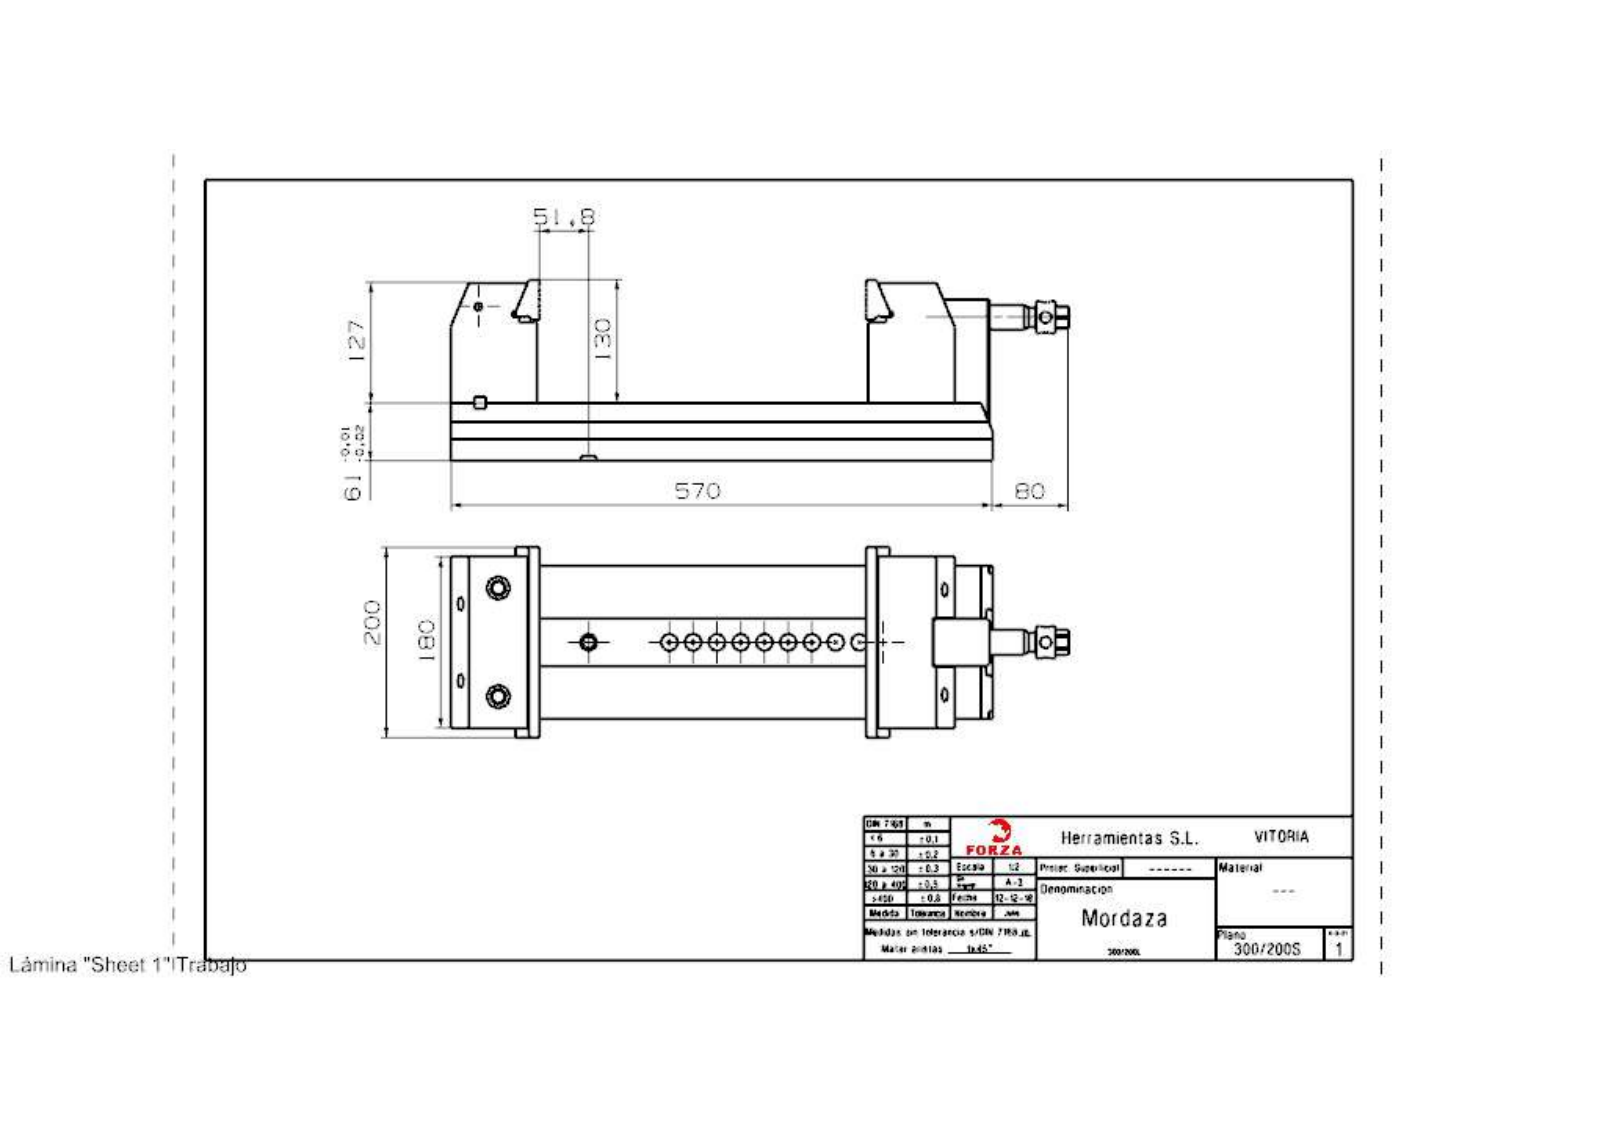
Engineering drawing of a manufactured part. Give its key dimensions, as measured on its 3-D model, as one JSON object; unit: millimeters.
{"part_name": "300_200S_Mordaza", "step_written_by": "SIEMENS PLM Software NX 11.0 (AUTOMOTIVE_DESIGN)", "units": "millimeters", "bodies": {"solids": 10, "faces": 481, "planar": 268, "cylindrical": 138, "other": 75}, "overall_size": [650, 200, 191], "volume_mm3": 8427000, "surface_area_mm2": 743184, "round_holes": [[15, 6], [5.19, 5], [13, 5], [6.99, 4], [8.5, 4], [10, 4], [8.78, 3], [10.58, 3], [19, 3], [12, 2], [12.38, 2], [14.38, 2]], "round_bosses_or_shafts": [[34, 1], [33.8, 1], [26, 1], [20, 1], [16.5, 1]], "partial_cylinders_radius": [[0.4, 24], [1.5, 4], [8, 4], [20, 4], [1.6, 2], [6, 2], [7, 2], [4, 1]], "face_to_face_distances": [61, 10, 170, 59.5, 29.2, 31.8, 7.5, 439, 91, 1.5], "hole_center_spacings": [14.5, 95.5, 81, 110, 110.72, 16.51, 16.55, 30]}
